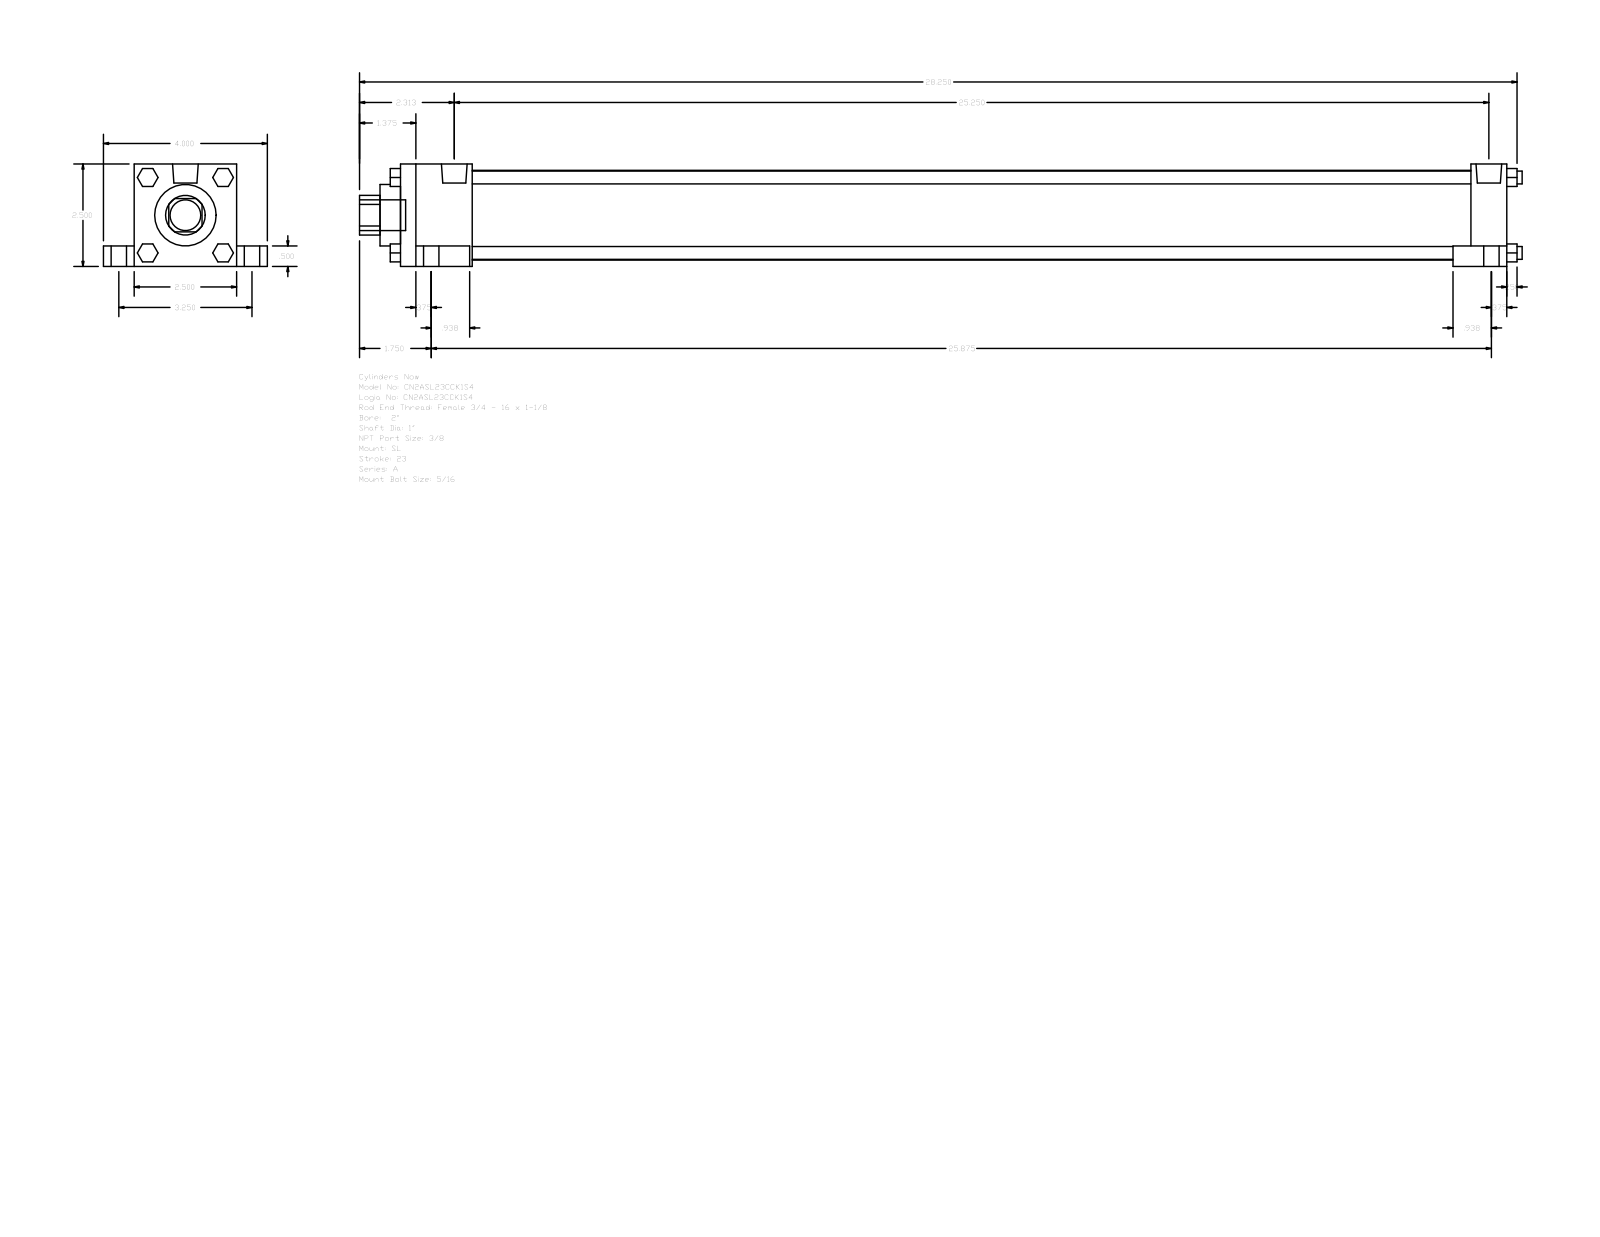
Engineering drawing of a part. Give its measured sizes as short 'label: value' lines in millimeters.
name: A_SL__0200_1
written by: GSSL Pune (CONFIG_CONTROL_DESIGN)
unit: mm
bodies: 0 solids, 148 faces (112 planar, 36 cylindrical, 0 other)
size: 720.73 × 101.6 × 63.5
holes: 1× ⌀25.4, 1× ⌀38.1, 1× ⌀55.63
bosses: 4× ⌀15.88, 4× ⌀9.53, 4× ⌀7.94, 4× ⌀5.56, 2× ⌀15.93, 1× ⌀19.05
rounds: 1× R12.29
face distances: 63.5, 12.7, 685.8, 50.8, 22.22, 19.05, 82.55, 44.45, 641.35, 663.58
